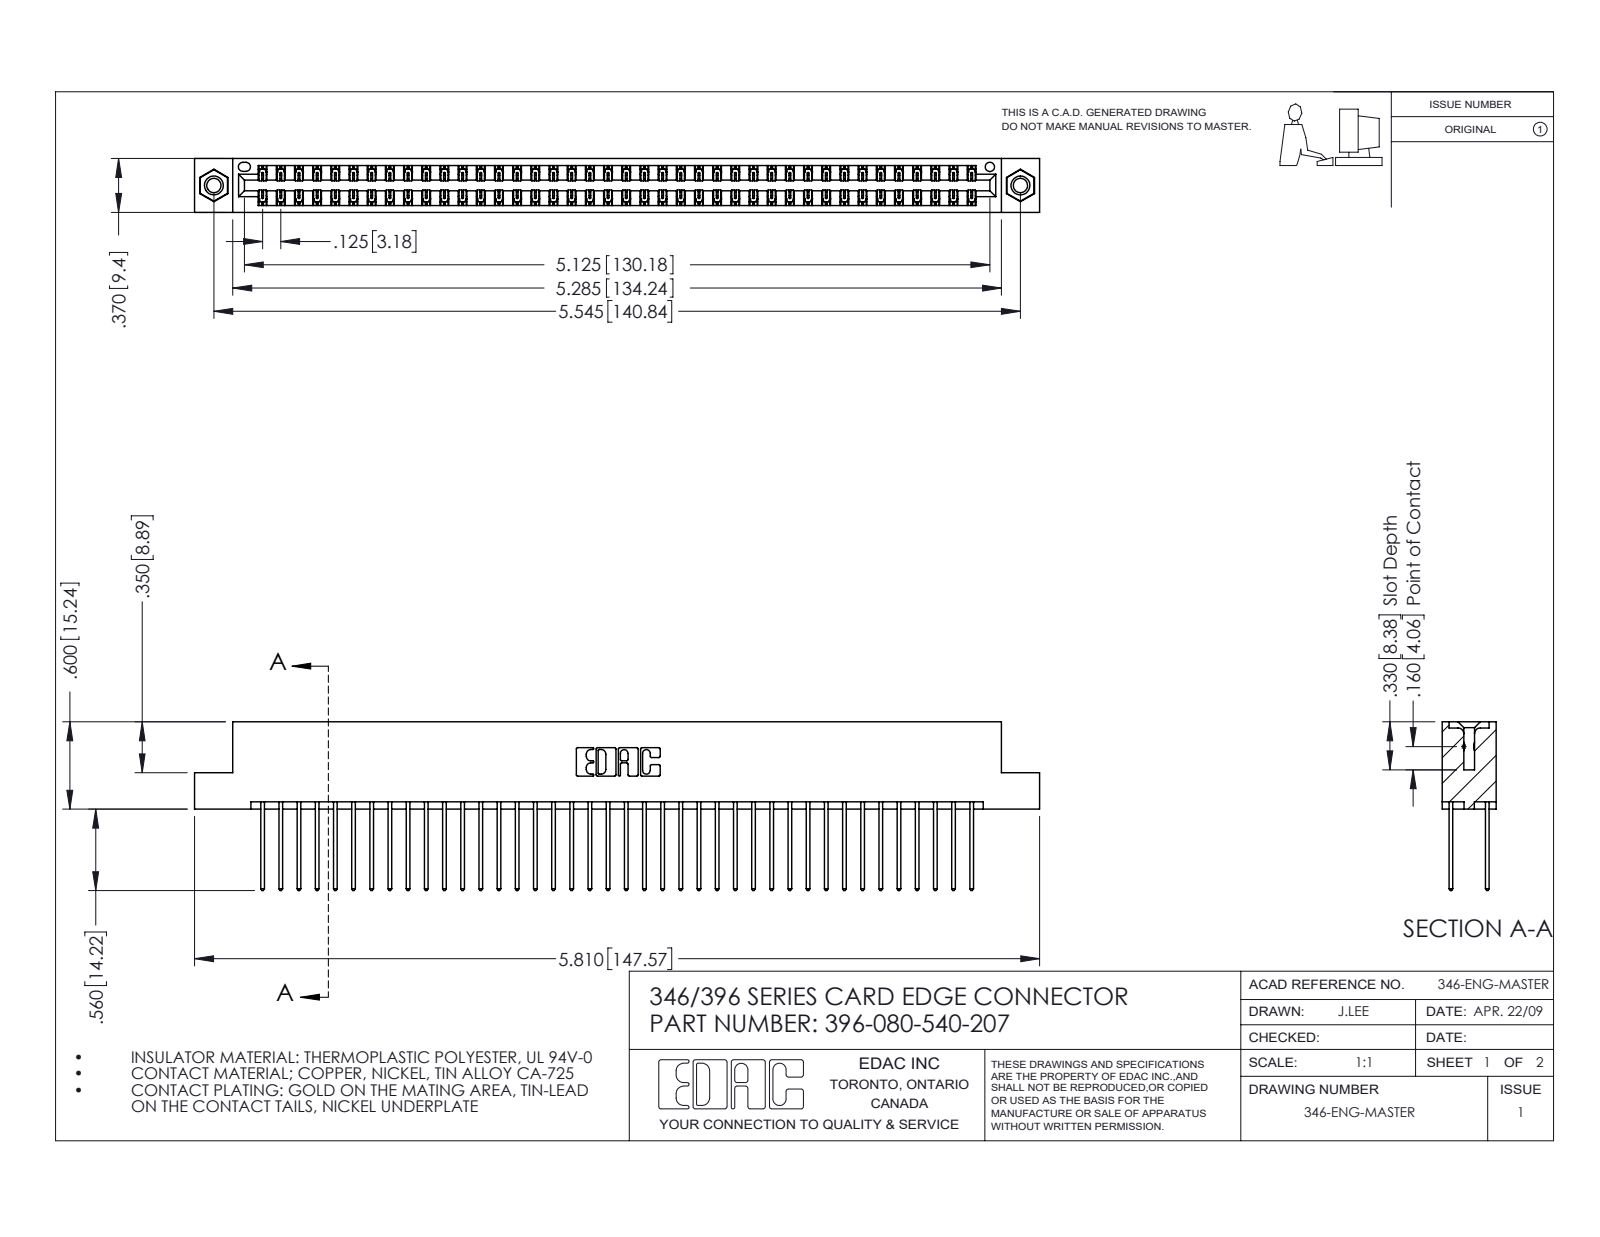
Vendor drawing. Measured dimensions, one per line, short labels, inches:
name: 346 Part_Flush Mounting Lugs - 0.156 Dia-TI; 396-080-540-207; 345-250-001_345-250-005-103; 345-292-001_345-293-140
written by: SolidWorks 2016 (CONFIG_CONTROL_DESIGN)
unit: in
bodies: 83 solids, 4342 faces (2908 planar, 1418 cylindrical, 16 other)
size: 5.81 × 1.16 × 0.37
volume: 0.895 in³; area: 33.47 in²
holes: 2× ⌀0.098, 2× ⌀0.125, 2× ⌀0.156, 1× ⌀0.064
bosses: 2× ⌀0.155
rounds: 120× R0.006, 80× R0.01, 22× R0.01, 6× R0.007, 6× R0.031, 3× R0.026, 2× R0.014, 2× R0.022
face distances: 0.048, 0.322, 0.25, 0.072, 0.298, 0.025, 0.37, 0.275, 0.148, 0.222
hole spacings: 0.246, 5.336, 5.545
